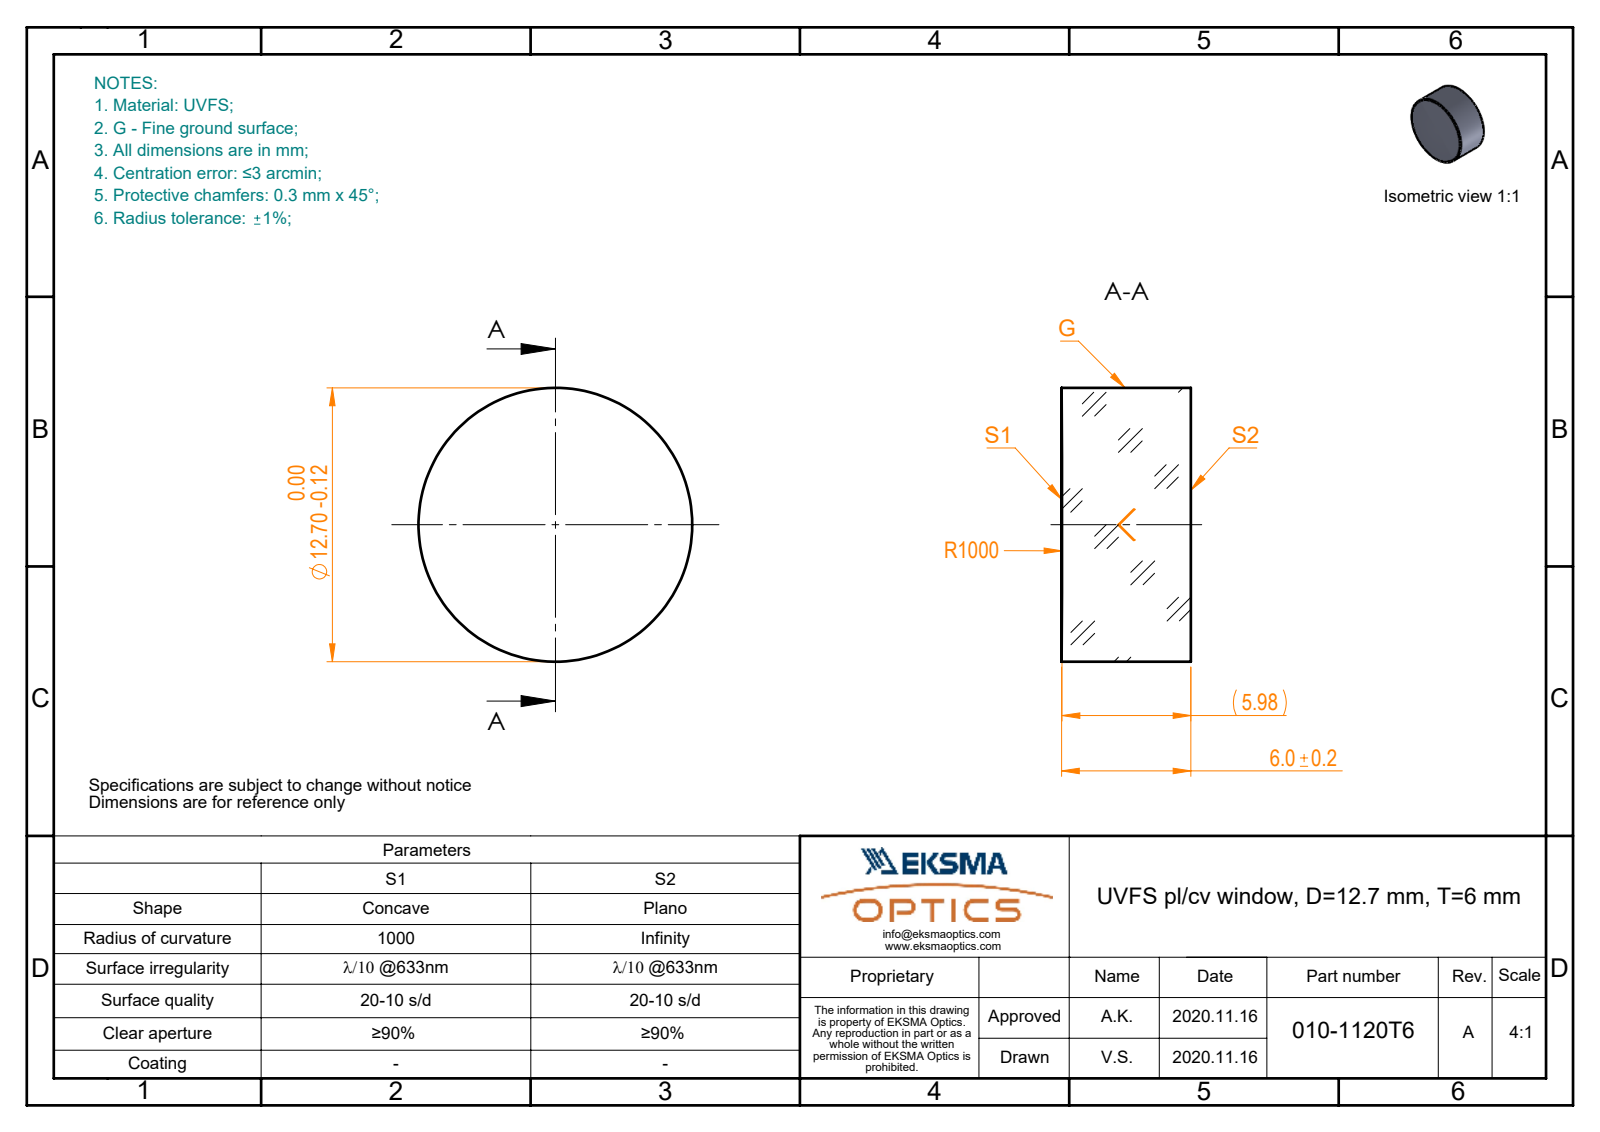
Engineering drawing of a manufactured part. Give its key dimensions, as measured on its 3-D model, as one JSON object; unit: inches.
{"part_name": "010-1120T6_UVFS_PCV_window", "step_written_by": "SolidWorks 2019 (CONFIG_CONTROL_DESIGN)", "units": "inches", "bodies": {"solids": 1, "faces": 5, "planar": 1, "cylindrical": 2, "other": 2}, "overall_size": [0.5, 0.5, 0.236], "volume_in3": 0.046, "surface_area_in2": 0.764, "round_bosses_or_shafts": [[0.5, 1]]}
